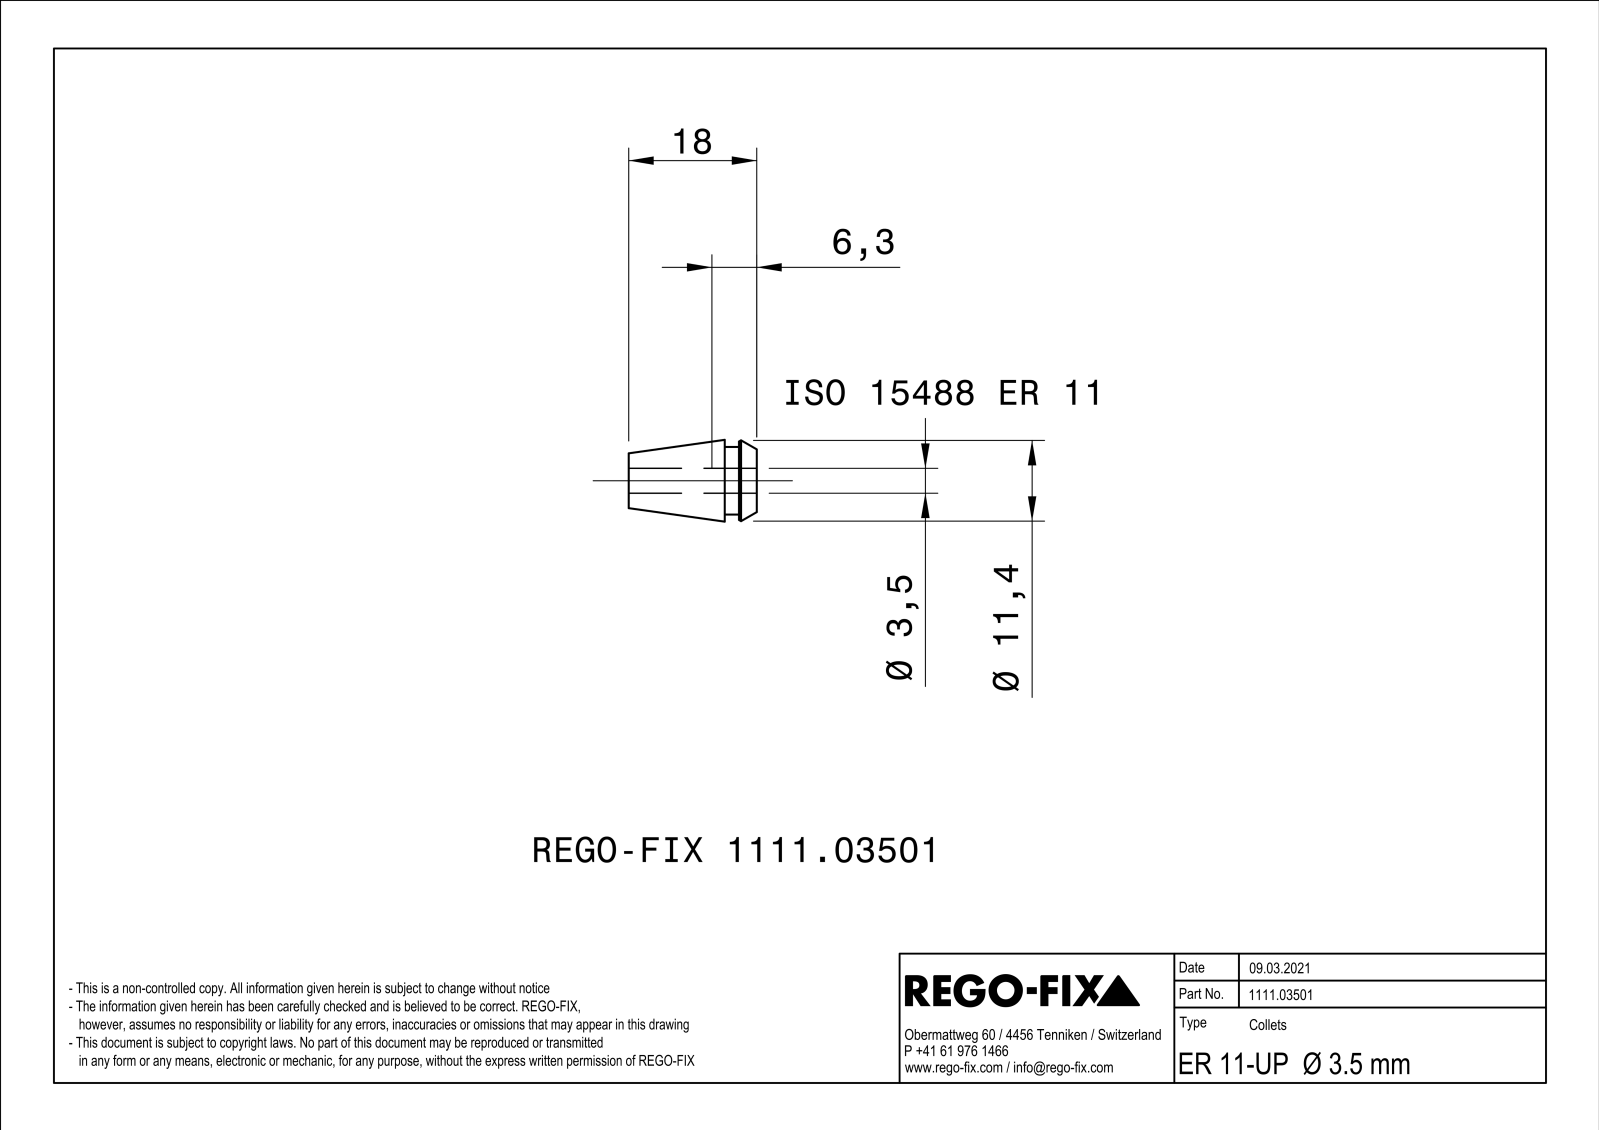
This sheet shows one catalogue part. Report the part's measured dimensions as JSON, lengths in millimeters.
{"part_name": "NOCUT", "step_written_by": "SIEMENS PLM Software Solid Edge ST10 (AUTOMOTIVE_DESIGN)", "units": "millimeters", "bodies": {"solids": 1, "faces": 157, "planar": 66, "cylindrical": 37, "other": 54}, "overall_size": [18, 11.5, 11.49], "volume_mm3": 926, "surface_area_mm2": 1819, "round_holes": [[3.5, 1]], "round_bosses_or_shafts": [[11.5, 1], [9.5, 1]], "partial_cylinders_radius": [[25, 12]], "face_to_face_distances": [0.45, 0.46, 0.44, 2.5, 18, 15.5, 4.5, 2, 13.5, 4]}
